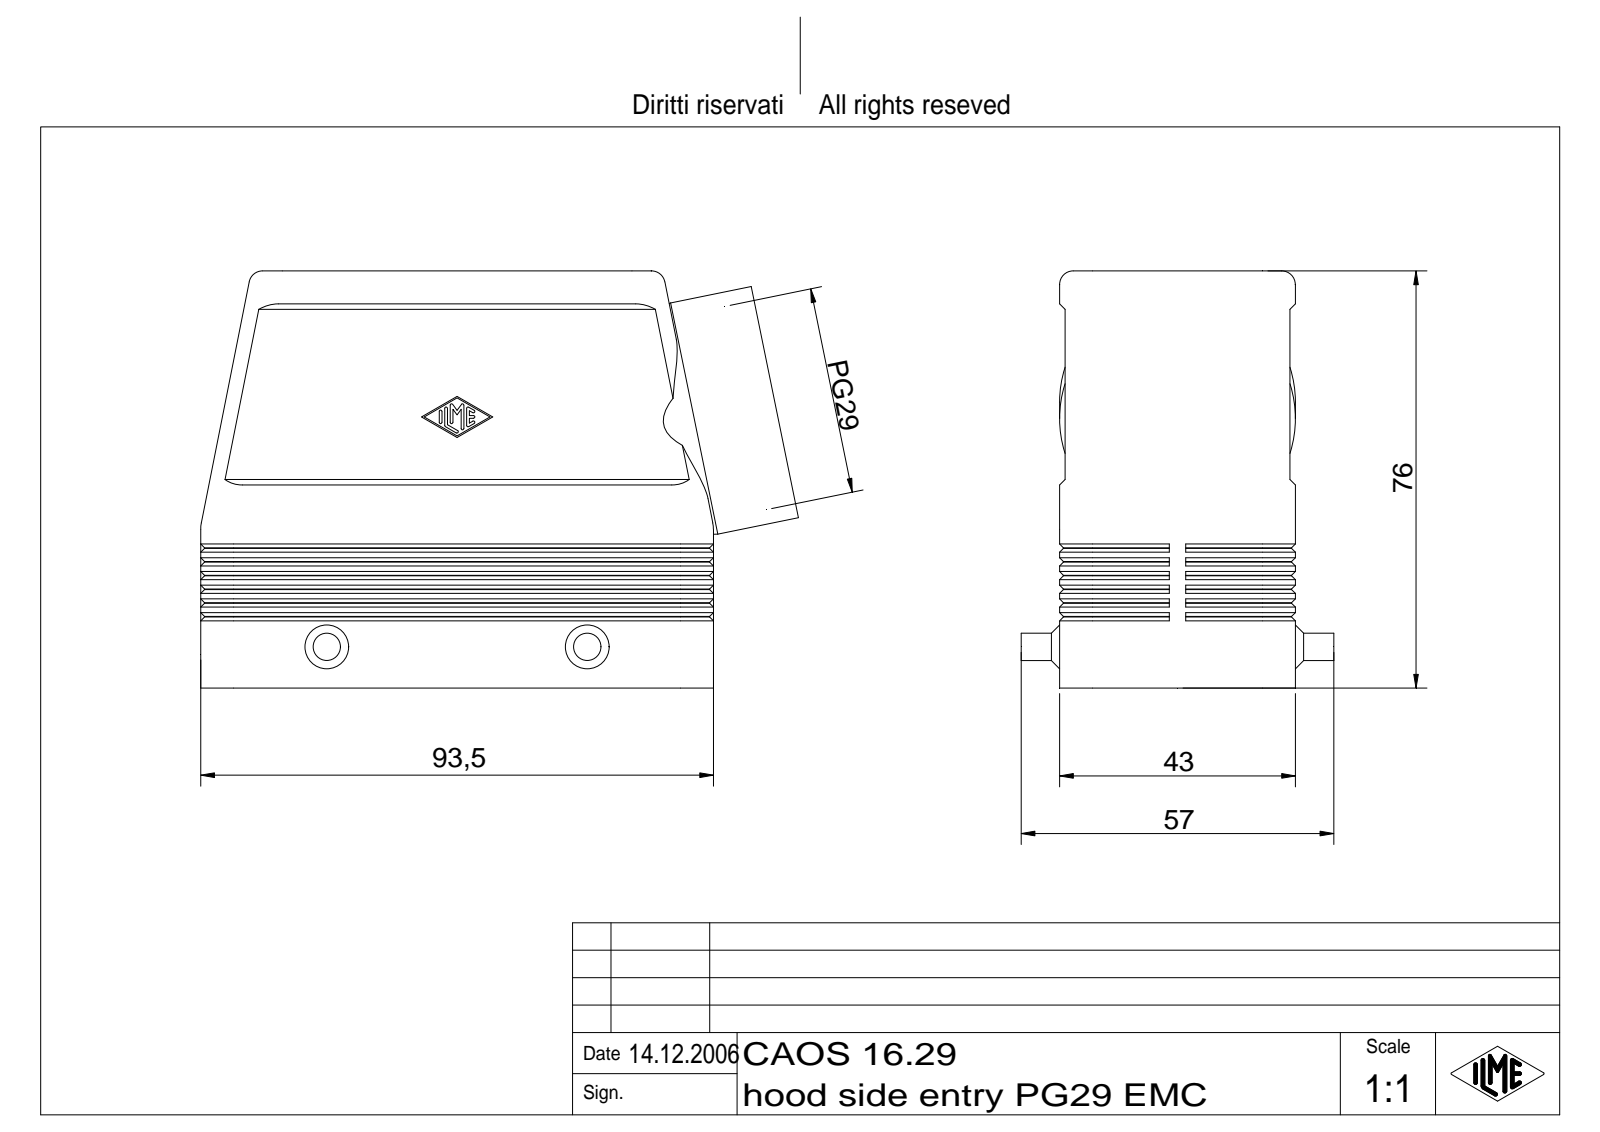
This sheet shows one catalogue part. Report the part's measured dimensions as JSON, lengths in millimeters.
{"part_name": "CAO Tüllengehäuse 2 Bügel für einen Einsatz", "step_written_by": "Autodesk Inventor 7 (AUTOMOTIVE_DESIGN)", "units": "millimeters", "bodies": {"solids": 1, "faces": 526, "planar": 192, "cylindrical": 134, "other": 200}, "overall_size": [108.99, 76, 57], "volume_mm3": 75719, "surface_area_mm2": 47322, "round_holes": [[33.48, 1], [35.48, 1]], "round_bosses_or_shafts": [[5, 2], [43, 1]], "partial_cylinders_radius": [[0.25, 14], [6, 10], [2, 4], [2.5, 4], [3, 4], [5.3, 2]], "face_to_face_distances": [3, 37, 2, 39, 1, 42, 40, 41, 43, 1.77]}
